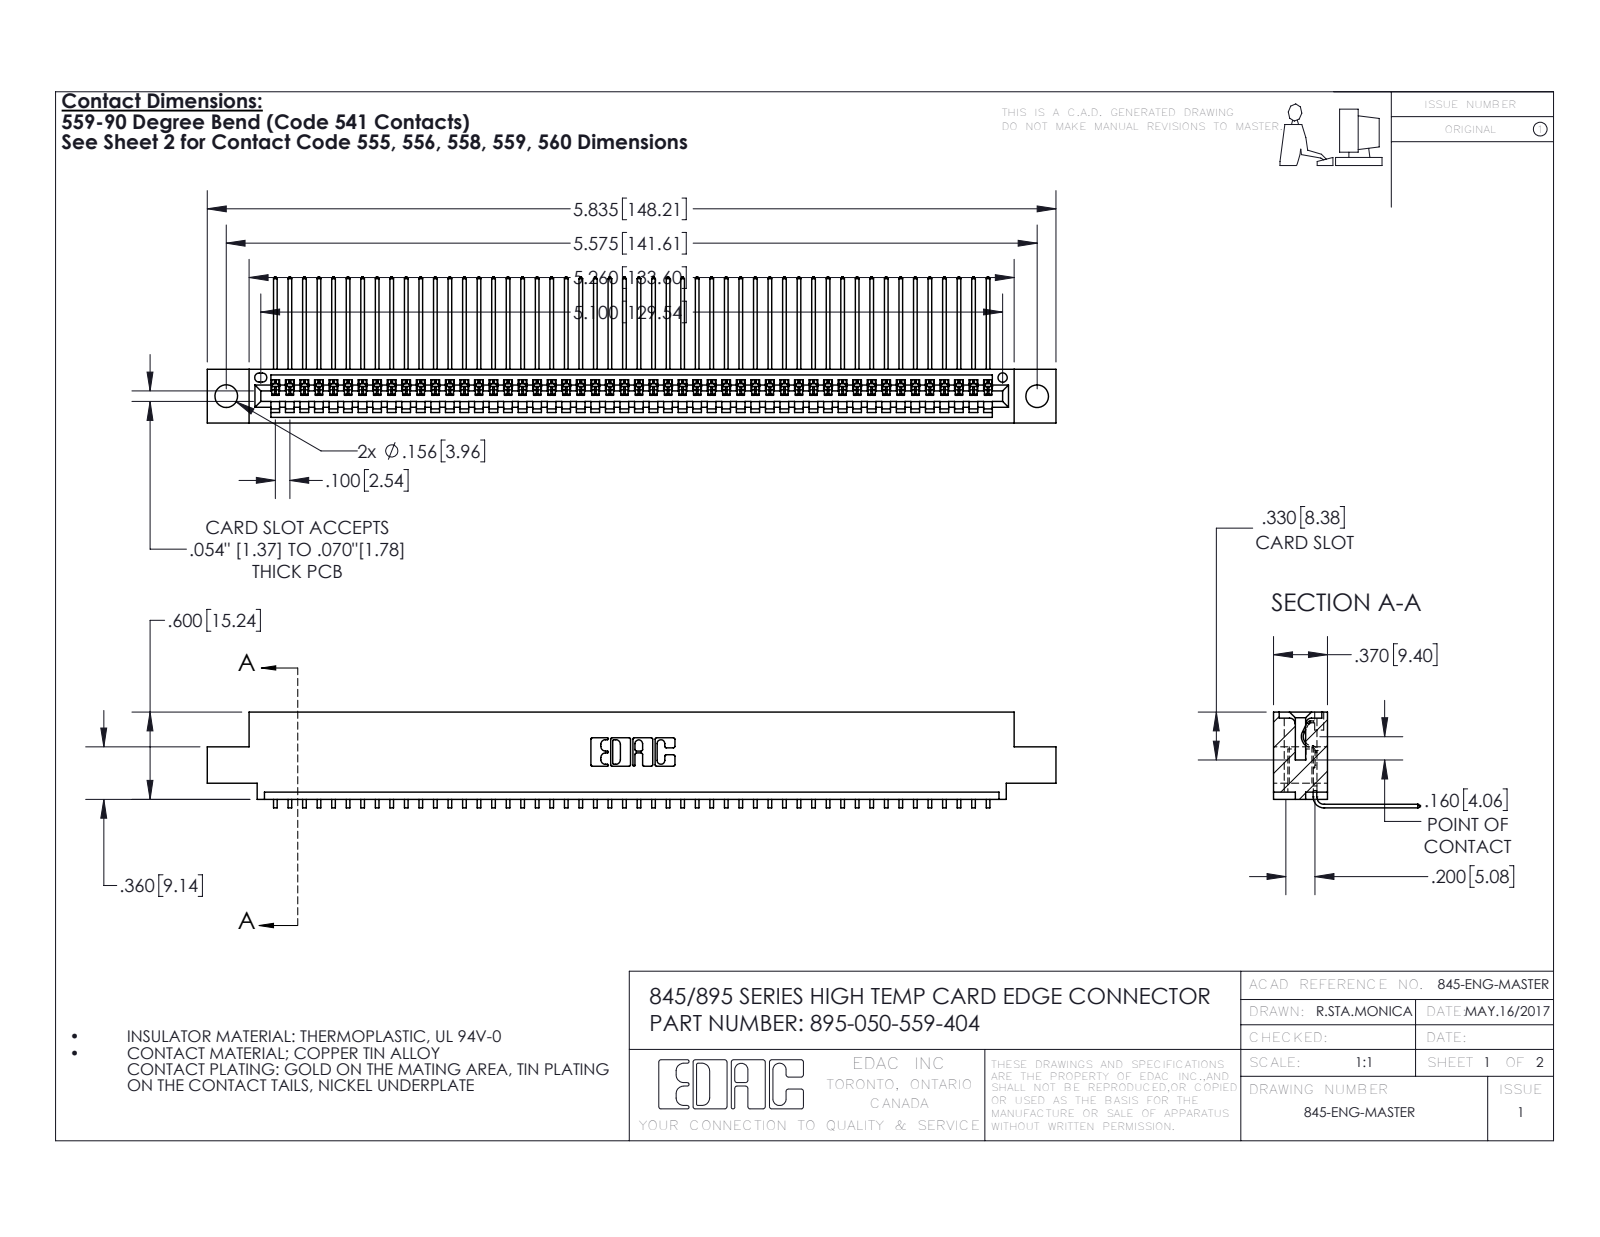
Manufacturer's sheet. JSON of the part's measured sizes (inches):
{"part_name": "395-050-559-404; 345 Part_0.110 Offset - 0.156 Dia-TH; 345-292-001_558 559 Tail - 1", "step_written_by": "SolidWorks 2016 (CONFIG_CONTROL_DESIGN)", "units": "inches", "bodies": {"solids": 51, "faces": 3130, "planar": 2184, "cylindrical": 946, "other": 0}, "overall_size": [5.835, 1.005, 0.659], "volume_in3": 0.863, "surface_area_in2": 30.66, "round_holes": [[0.156, 2], [0.064, 1]], "partial_cylinders_radius": [[0.006, 100], [0.01, 22], [0.007, 6], [0.031, 6], [0.026, 3], [0.031, 2], [0.04, 2], [0.014, 1]], "face_to_face_distances": [0.072, 0.298, 0.37, 0.2, 0.098, 0.272, 0.025, 0.225, 0.149, 0.072], "hole_center_spacings": [0.27, 5.339, 5.575]}
